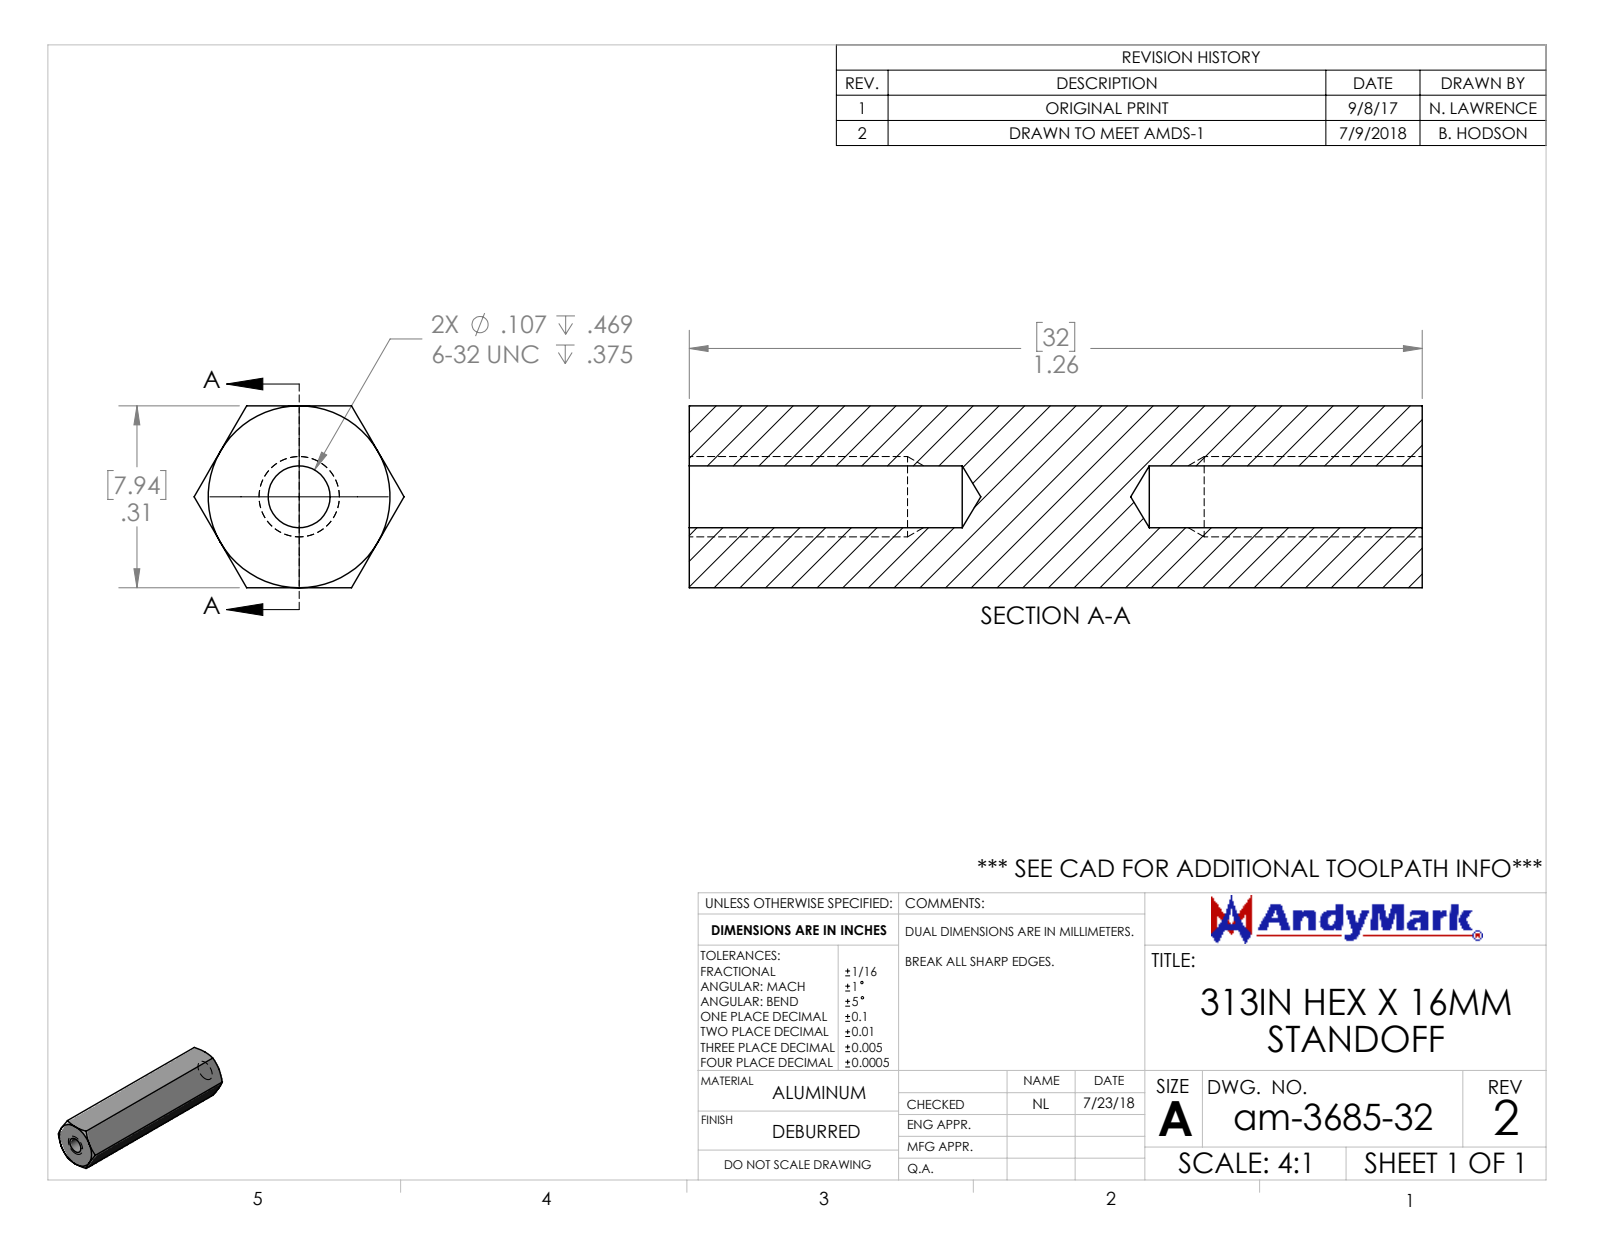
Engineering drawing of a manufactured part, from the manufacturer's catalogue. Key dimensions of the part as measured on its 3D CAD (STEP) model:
Part name (STEP PRODUCT): am-3685-32 .3125IN Hex Standoff, 32mm Long REV2
STEP written by: SolidWorks 2018 (AUTOMOTIVE_DESIGN)
Units: inches
Bodies: 1 solid, 30 faces (8 planar, 4 cylindrical, 18 other)
Overall size (bounding box): 1.26 × 0.361 × 0.313
Volume: 0.098 in³ · Surface area: 1.842 in²
Round holes (diameter × count): ⌀0.107 ×1
Main face-to-face distances: 0.313, 1.26
